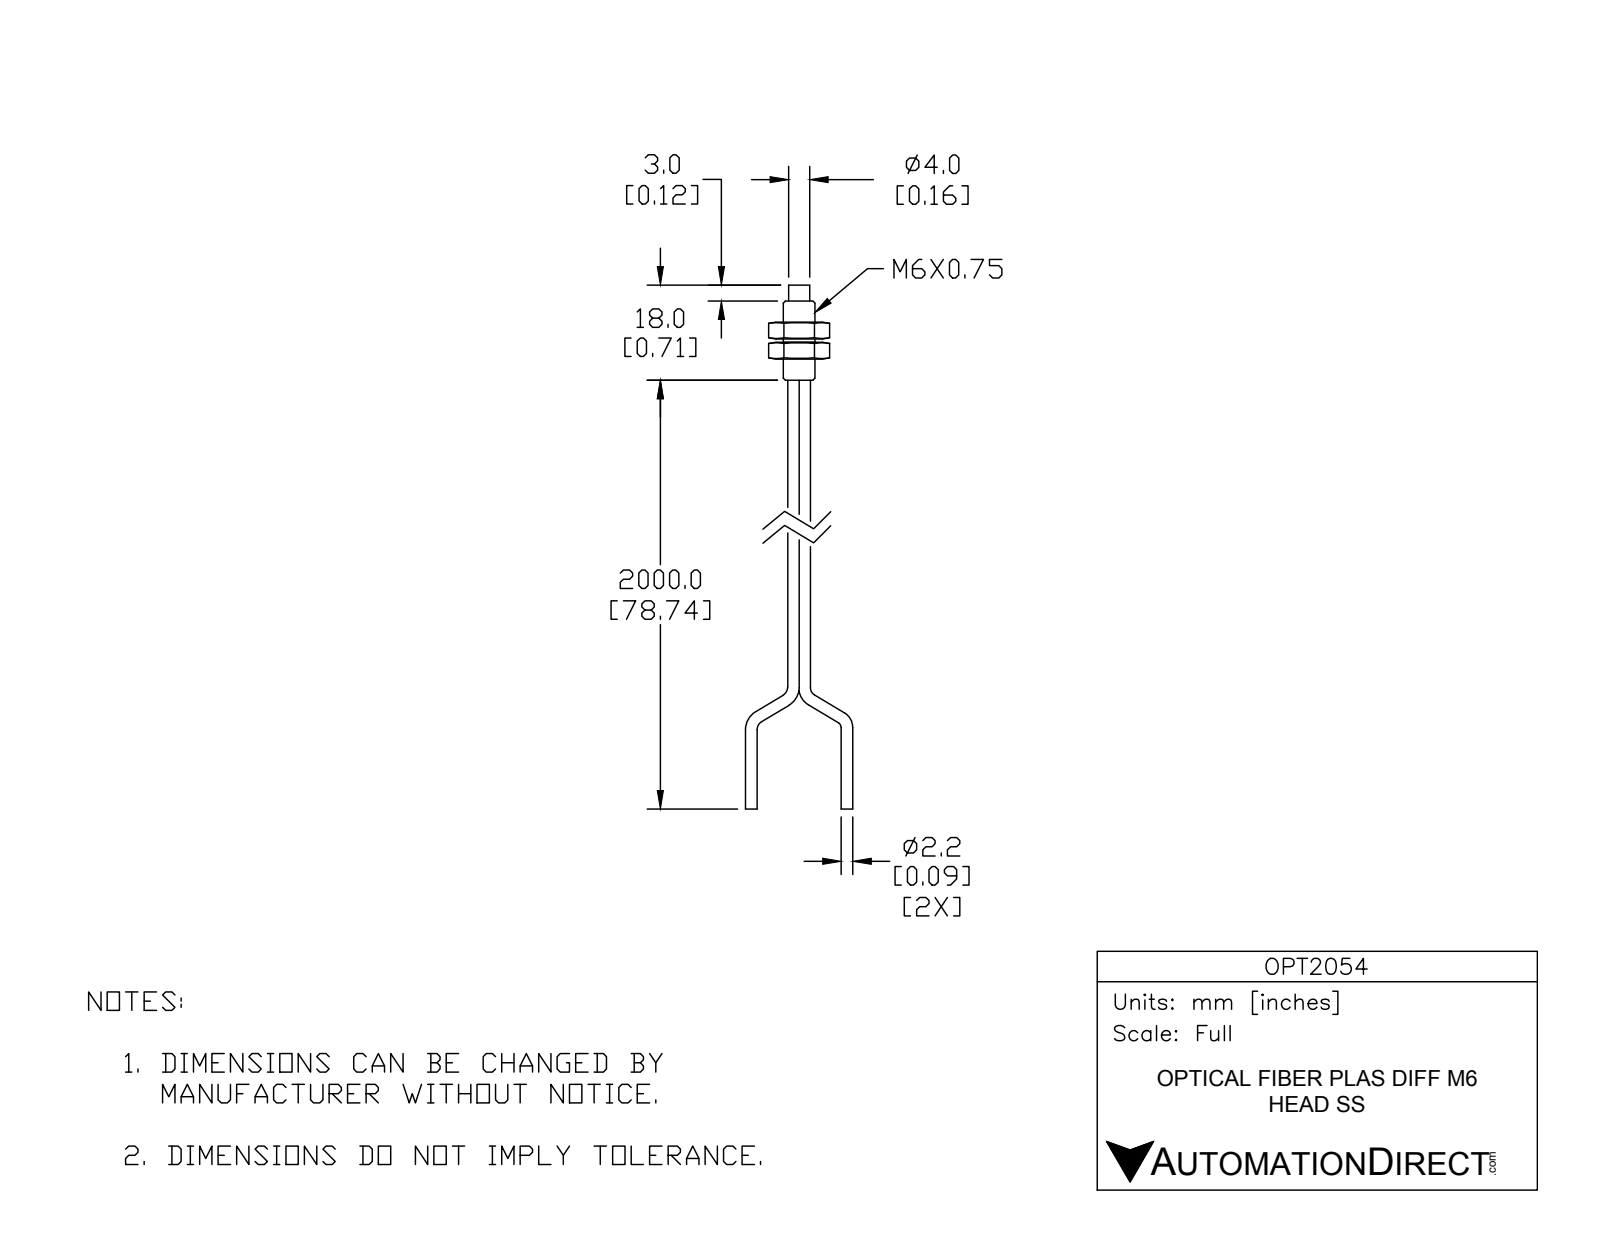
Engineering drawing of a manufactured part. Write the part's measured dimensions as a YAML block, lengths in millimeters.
part_name: "OPT2054"
step_written_by: "SolidWorks 2014 (AUTOMOTIVE_DESIGN)"
units: millimeters
bodies: {solids: 4, faces: 71, planar: 27, cylindrical: 24, other: 20}
overall_size: [99.1, 20.3, 10]
volume: 1400
surface_area: 1685
round_bosses_or_shafts:
  - {diameter: 2.2, count: 6}
  - {diameter: 6, count: 1}
  - {diameter: 4, count: 1}
face_to_face_distances: [10, 3.2, 3.8, 7, 0.6, 4, 7.2, 7.8, 11, 10.2]
